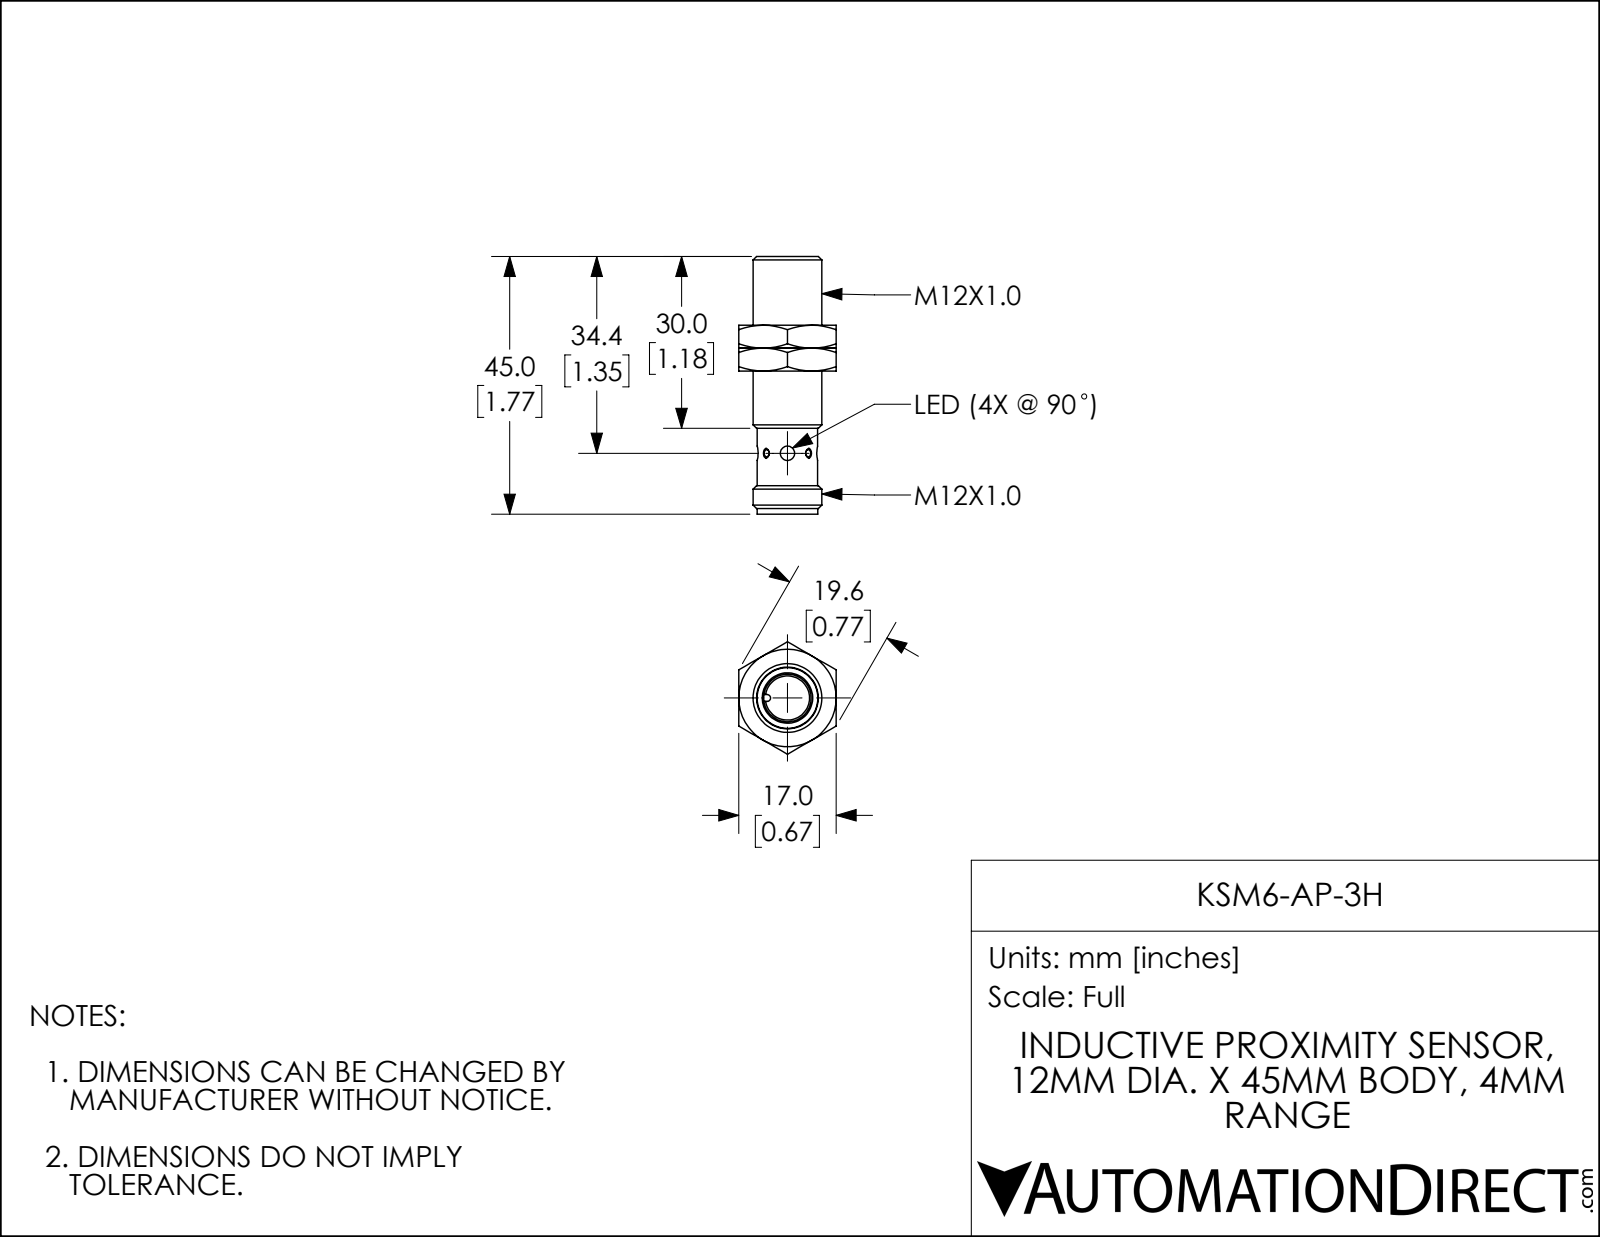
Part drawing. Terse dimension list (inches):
name: KSM6-AP-3H
written by: SolidWorks 2017 (AUTOMOTIVE_DESIGN)
unit: in
bodies: 3 solids, 88 faces (27 planar, 14 cylindrical, 47 other)
size: 1.772 × 0.773 × 0.669
volume: 0.336 in³; area: 5.341 in²
holes: 2× ⌀0.098, 1× ⌀0.327, 1× ⌀0.402, 1× ⌀0.43
bosses: 1× ⌀0.472, 1× ⌀0.417, 1× ⌀0.415, 1× ⌀0.4
rounds: 1× R0.024
face distances: 0.157, 0.669, 0.315, 0.787, 0.63, 0.472, 0.634, 0.791, 0.949, 1.421
